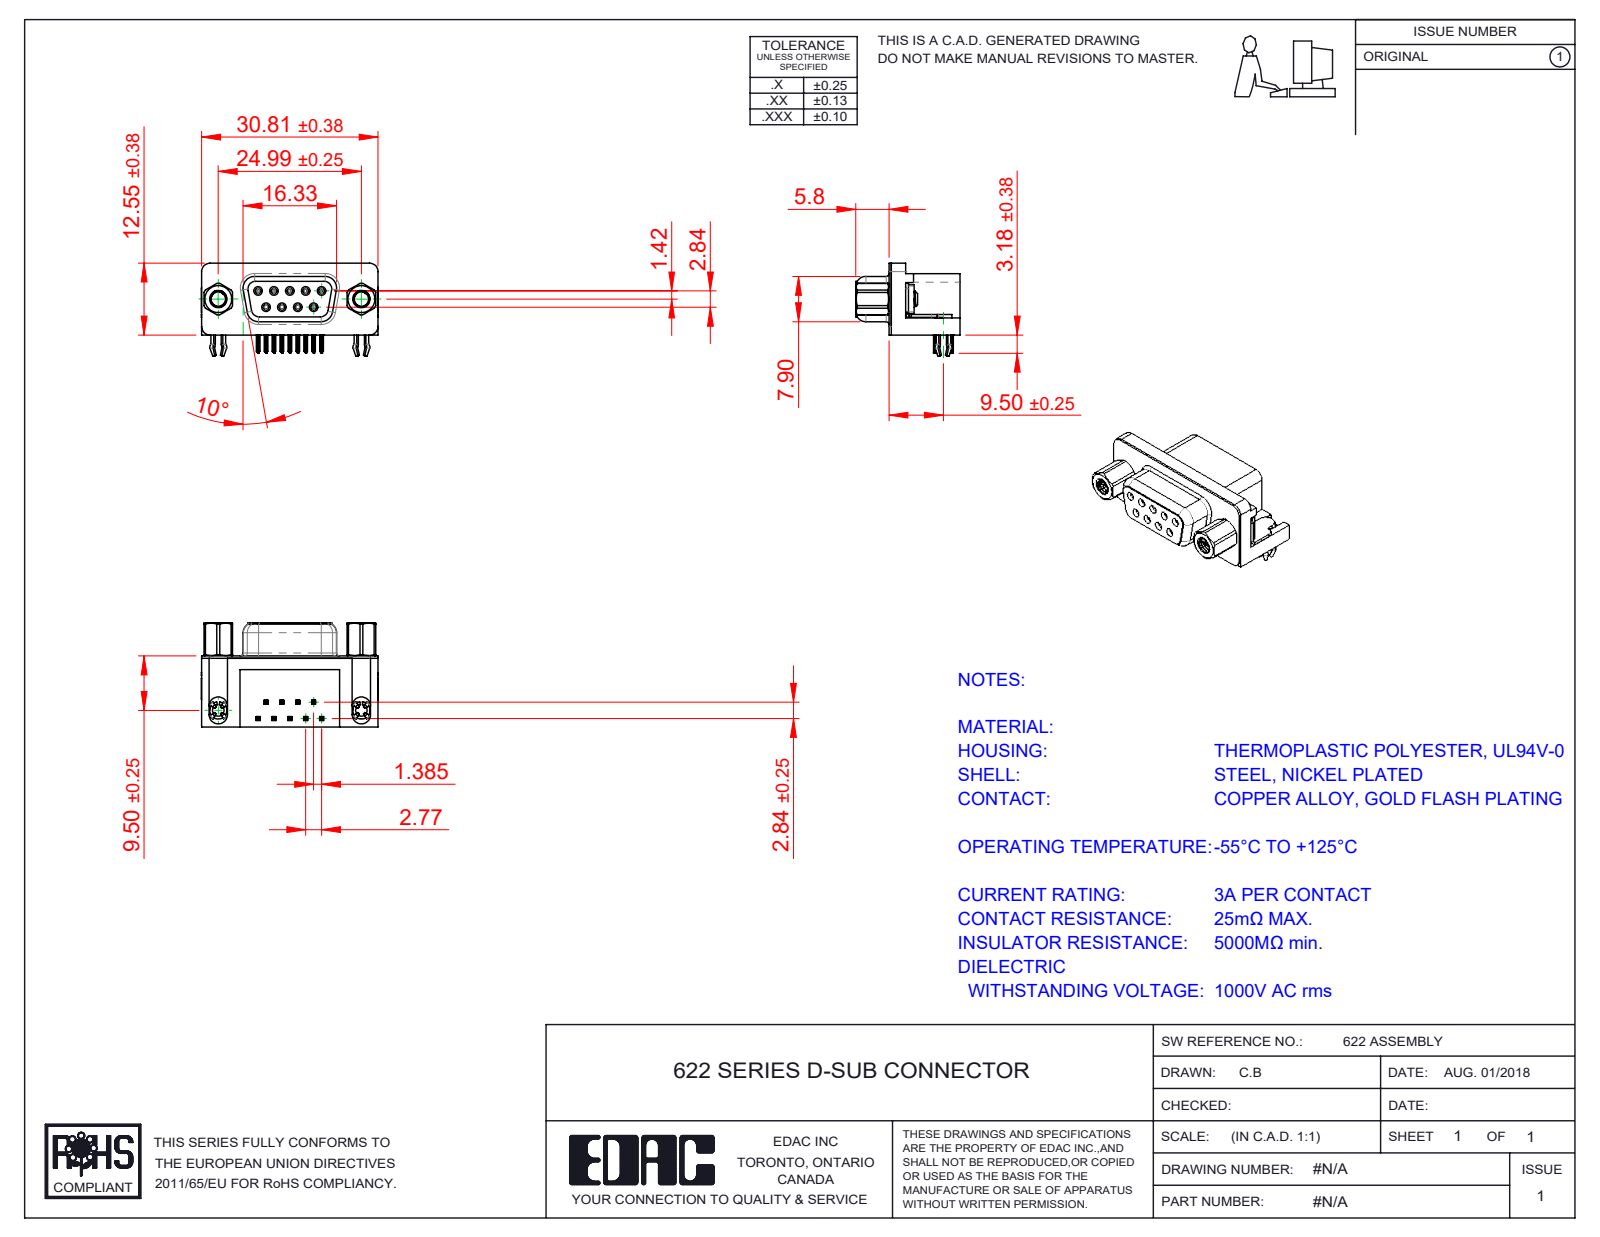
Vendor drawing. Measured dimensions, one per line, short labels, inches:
name: 622 Contact Top; 622 Housing_9 Socket; 622 4-40 Threaded Board Mount; 622 M3 Threaded Rivet (+3 more)
written by: SolidWorks 2016 (CONFIG_CONTROL_DESIGN)
unit: in
bodies: 15 solids, 1602 faces (684 planar, 432 cylindrical, 486 other)
size: 1.216 × 0.717 × 0.619
volume: 0.228 in³; area: 7.992 in²
holes: 9× ⌀0.031, 9× ⌀0.035, 2× ⌀0.089, 2× ⌀0.098, 2× ⌀0.157, 2× ⌀0.189, 2× ⌀0.197
bosses: 9× ⌀0.047, 2× ⌀0.193, 2× ⌀0.187, 2× ⌀0.154, 2× ⌀0.128
rounds: 72× R0.004, 36× R0.006, 18× R0.014, 18× R0.039, 9× R0.013, 8× R0.01, 8× R0.053, 8× R0.063
face distances: 0.016, 0.472, 0.488, 0.014, 0.114, 0.098, 0.244, 0.407, 0.374, 0.228
hole spacings: 0.124, 0.109, 0.218, 0.198, 0.198, 0.327, 0.294, 0.295
